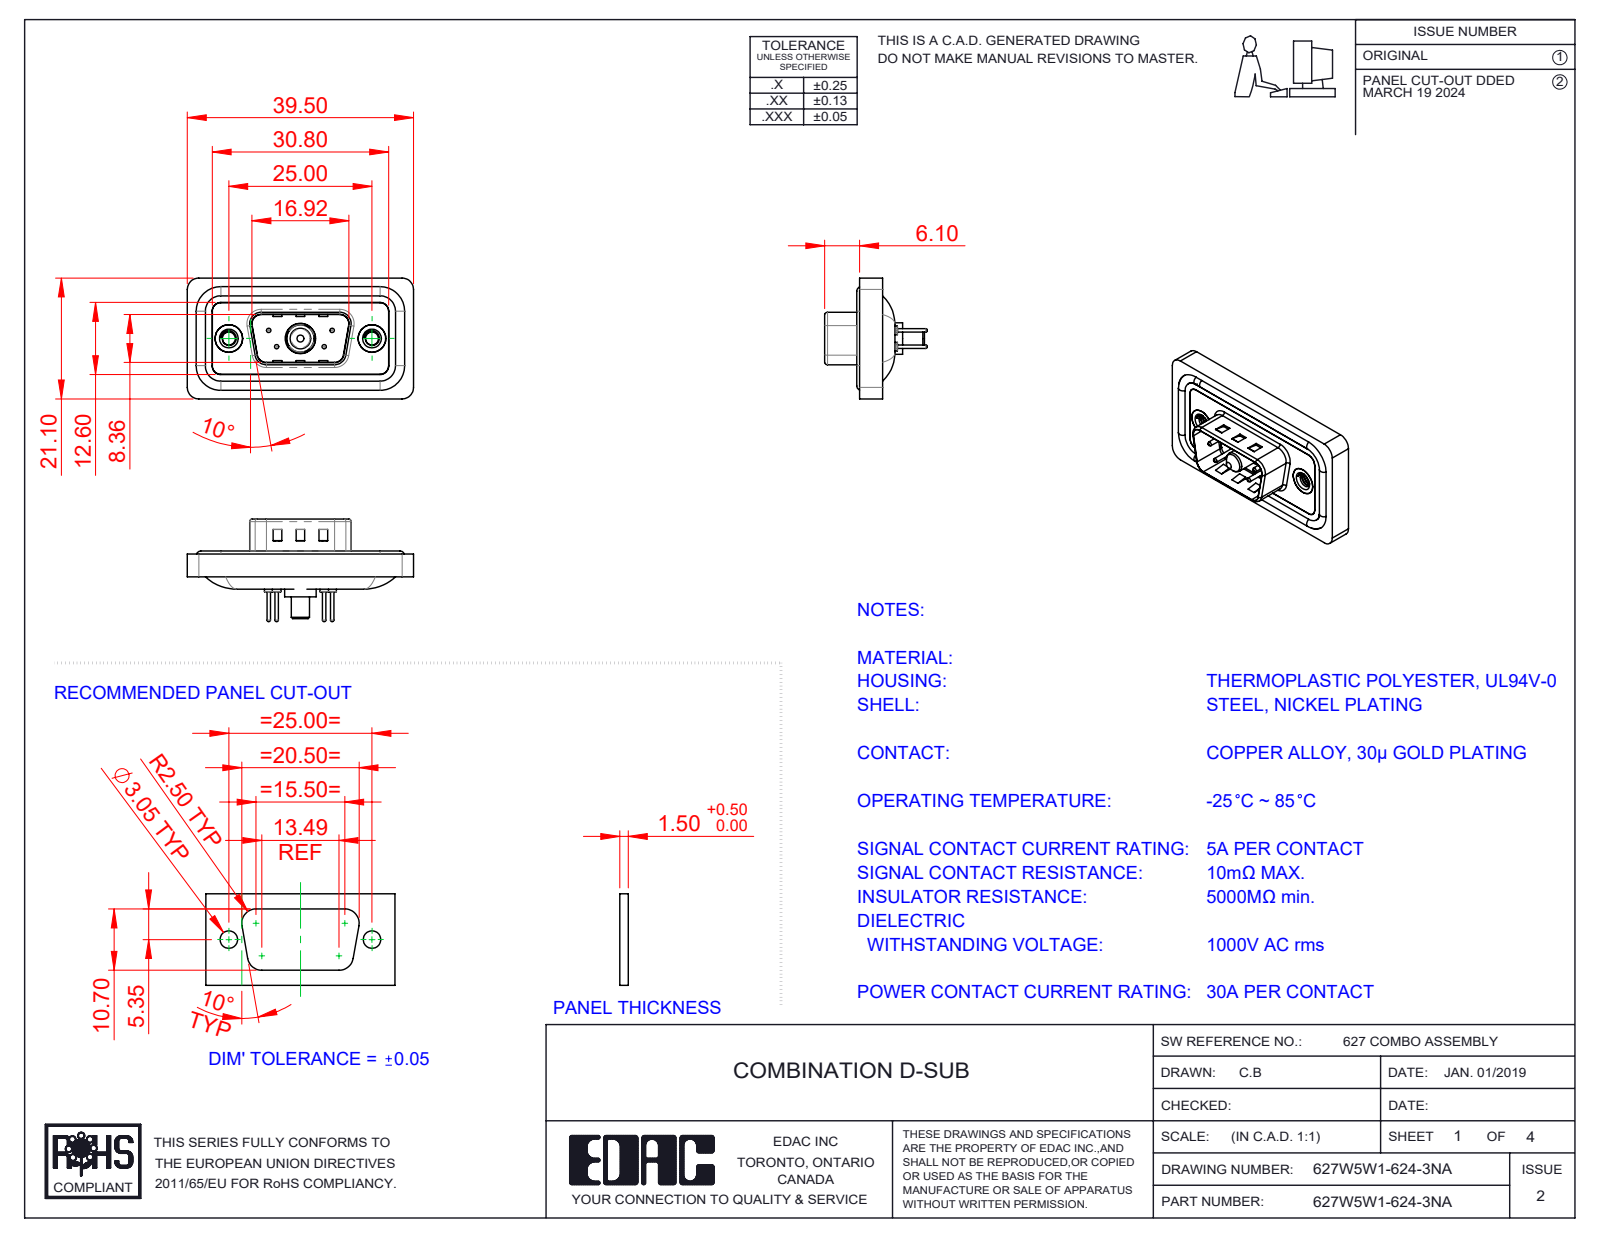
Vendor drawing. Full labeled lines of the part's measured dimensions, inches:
Part name (STEP PRODUCT): Power Pin_30A S; 627Combo Shell Rear_09 Contacts; 627Combo Threaded Rivet_A; 627Combo Contact Row 1_24 (+5 more)
STEP written by: SolidWorks 2023 (CONFIG_CONTROL_DESIGN)
Units: inches
Bodies: 13 solids, 596 faces (183 planar, 257 cylindrical, 156 other)
Overall size (bounding box): 1.555 × 0.831 × 0.705
Volume: 0.268 in³ · Surface area: 10.76 in²
Round holes (diameter × count): ⌀0.03 ×4, ⌀0.063 ×4, ⌀0.079 ×4, ⌀0.089 ×2, ⌀0.157 ×2, ⌀0.189 ×2, ⌀0.197 ×2, ⌀0.191 ×1, ⌀0.209 ×1
Round bosses / shafts (diameter × count): ⌀0.063 ×4, ⌀0.059 ×4, ⌀0.024 ×4, ⌀0.193 ×2, ⌀0.217 ×1, ⌀0.205 ×1, ⌀0.187 ×1, ⌀0.148 ×1
Partial cylindrical surfaces — rounded edges, fillets, slot ends (radius × count): R0.059 ×22, R0.079 ×18, R0.02 ×8, R0.063 ×8, R0.01 ×4, R0.024 ×4, R0.026 ×4, R0.035 ×4
Main face-to-face distances: 0.016, 0.043, 0.114, 0.063, 0.122, 0.059, 0.02, 0.098, 0.157, 0.031
Hole centre spacings: 0.124, 0.225, 0.28, 0.492, 0.713, 0.173, 0.173, 0.327
